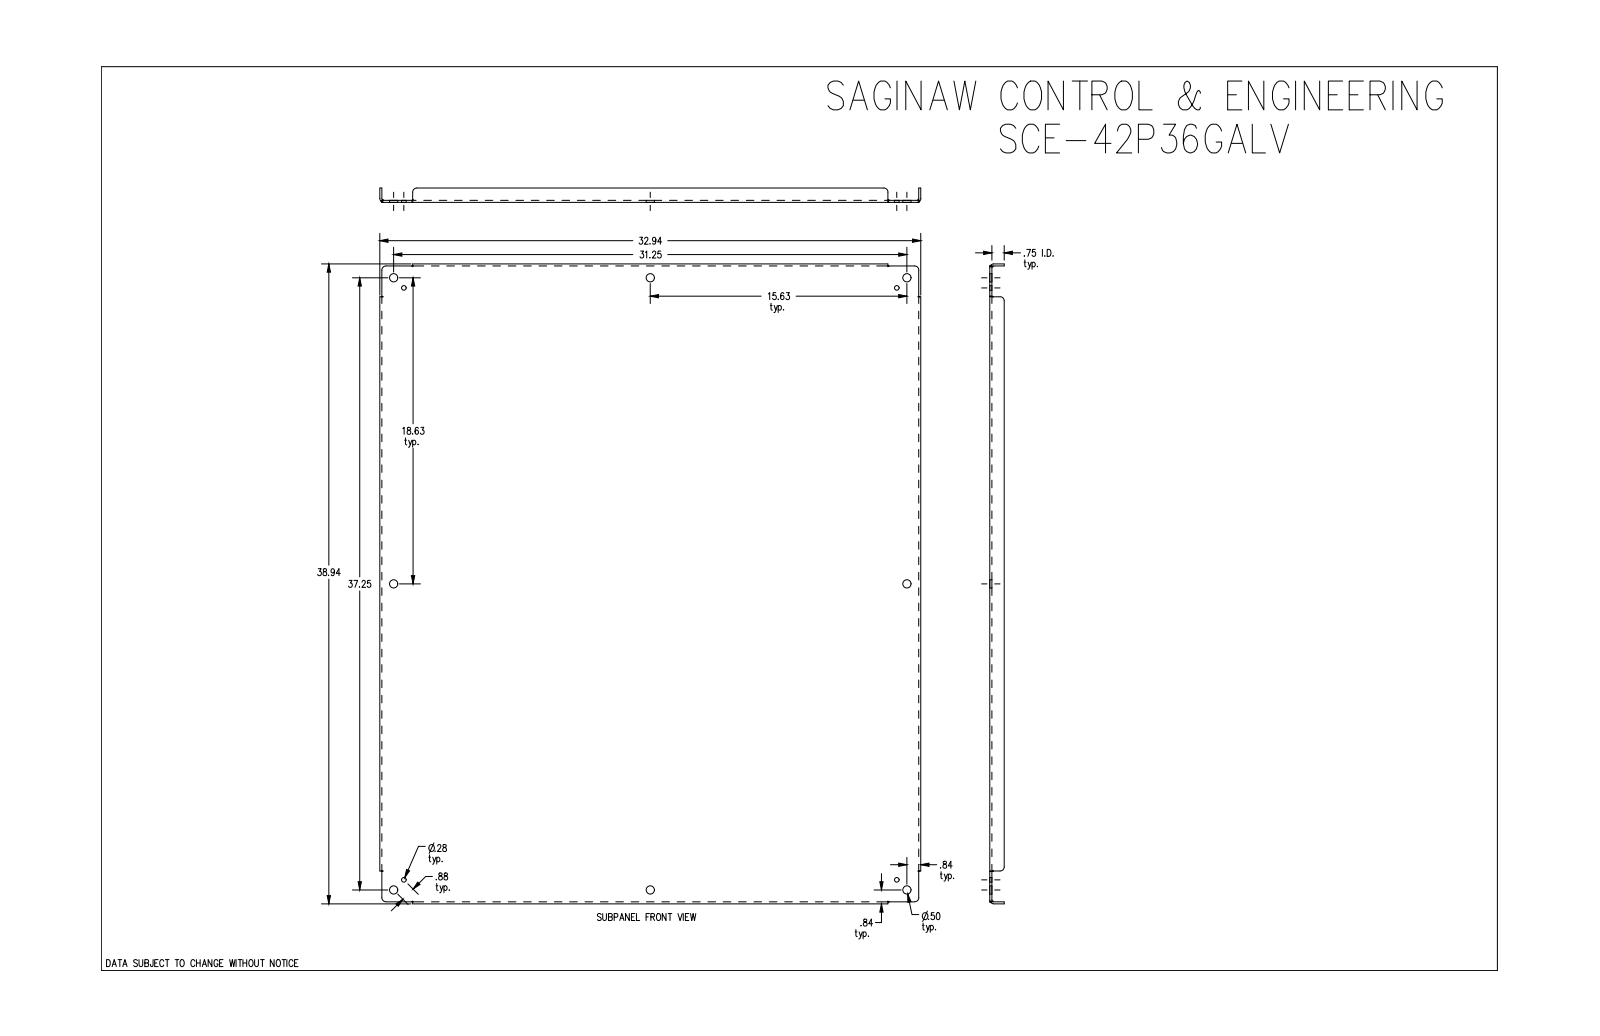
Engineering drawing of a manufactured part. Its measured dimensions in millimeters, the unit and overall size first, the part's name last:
Units: millimetres
Overall size (bounding box): 989 × 836.6 × 22.2
Round holes (diameter × count): ⌀12.7 ×8, ⌀7.1 ×4
Partial cylindrical surfaces — rounded edges, fillets, slot ends (radius × count): R6.4 ×8, R2.8 ×4, R6 ×4
Main face-to-face distances: 3.2, 3.2, 833.5, 985.9, 830.2, 836.6, 982.6, 989, 19.1, 22.2
Hole centre spacings: 22.2, 381.5, 396.9, 457.6, 473.1, 617.5, 778.2, 902.5
Volume: 2 796 000 mm³ · Surface area: 1 774 000 mm²
Bodies: 1 solid, 86 faces (30 planar, 32 cylindrical, 24 other)
Part name (STEP PRODUCT): SCE-42P36GALV
STEP written by: SolidWorks 2019 (CONFIG_CONTROL_DESIGN)
